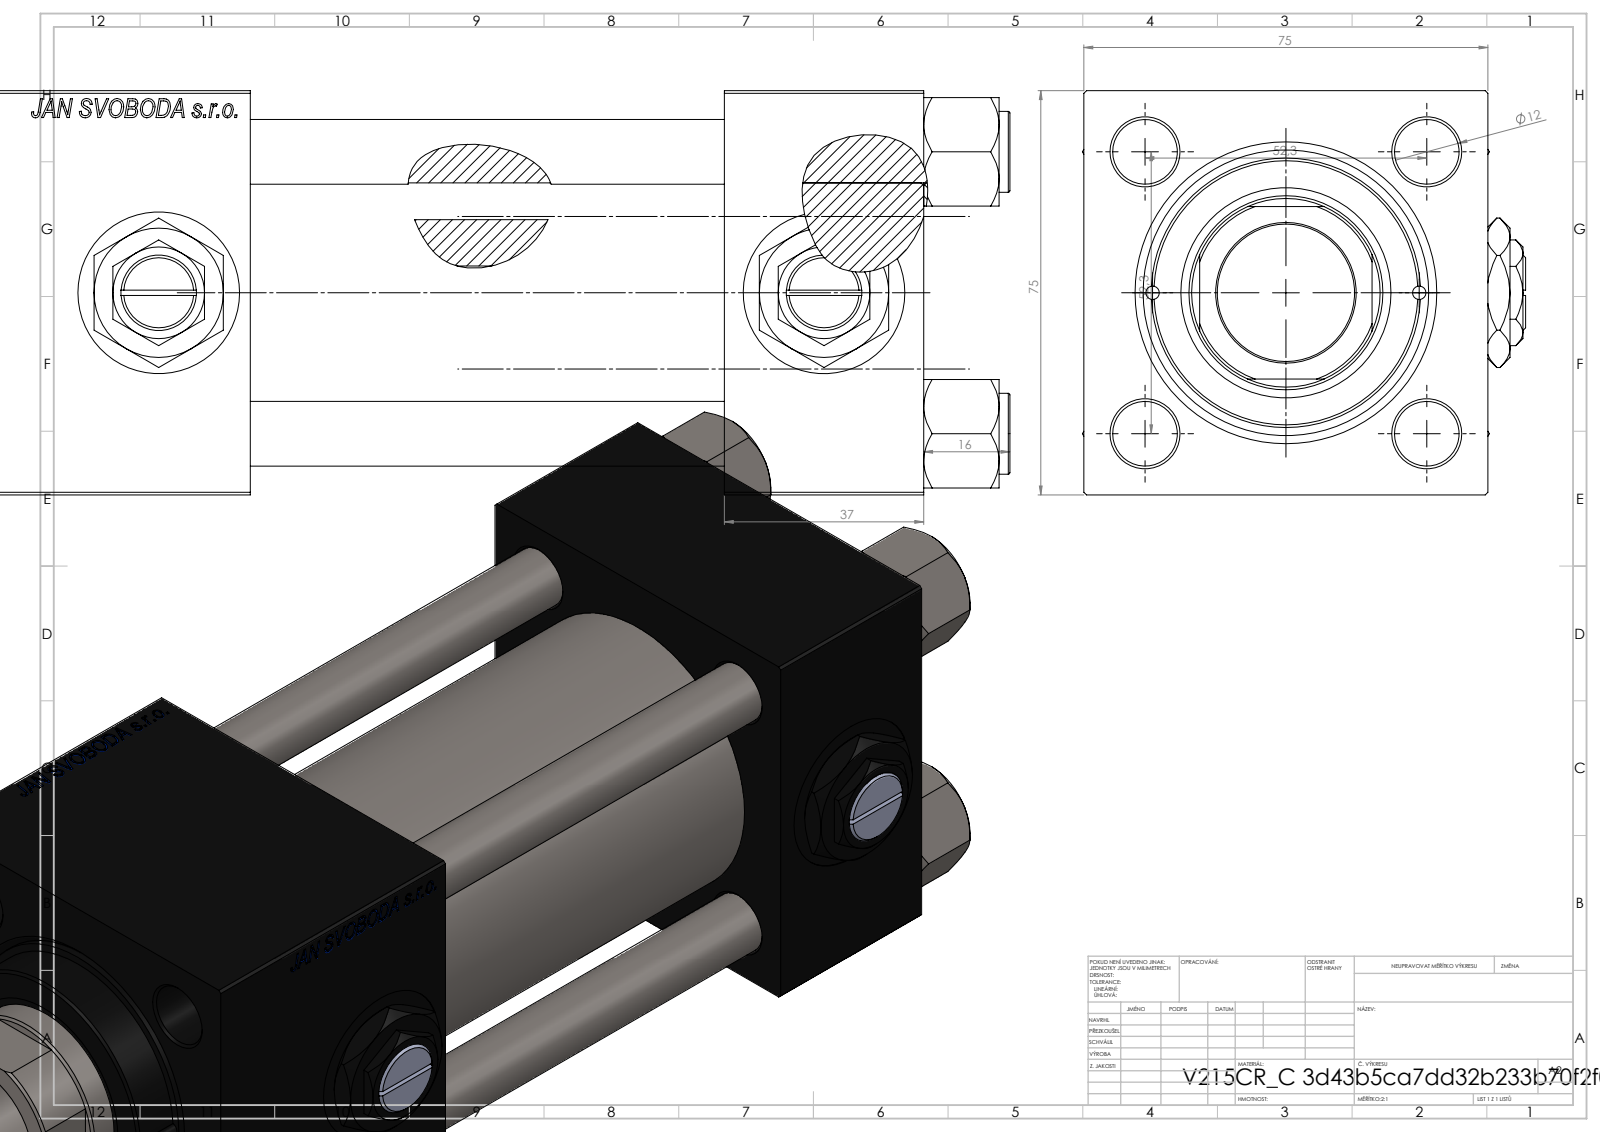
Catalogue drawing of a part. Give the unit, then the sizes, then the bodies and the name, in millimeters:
Units: millimetres
Overall size (bounding box): 225 × 82.27 × 75
Round holes (diameter × count): ⌀12 ×4, ⌀2.5 ×2, ⌀7 ×2, ⌀20.96 ×2, ⌀30 ×2, ⌀25.5 ×1, ⌀36 ×1, ⌀39 ×1, ⌀41 ×1, ⌀53 ×1
Round bosses / shafts (diameter × count): ⌀15 ×4, ⌀56 ×1, ⌀50 ×1
Partial cylindrical surfaces — rounded edges, fillets, slot ends (radius × count): R17.5 ×1
Main face-to-face distances: 75, 37, 125, 88, 59, 184, 147, 74.8, 155.3, 118.3
Hole centre spacings: 26.19, 36.98, 52.3, 57.22, 24.75, 73.96, 49.5, 123.5
Volume: 740 071 mm³ · Surface area: 178 002 mm²
Bodies: 13 solids, 1255 faces (575 planar, 102 cylindrical, 578 other)
Part name (STEP PRODUCT): V215CR_C_Body; V215_VC_A; V215CR_C_TYCINKA; V215CR_VCP_C (+2 more)
STEP written by: SolidWorks 2019 (CONFIG_CONTROL_DESIGN)
